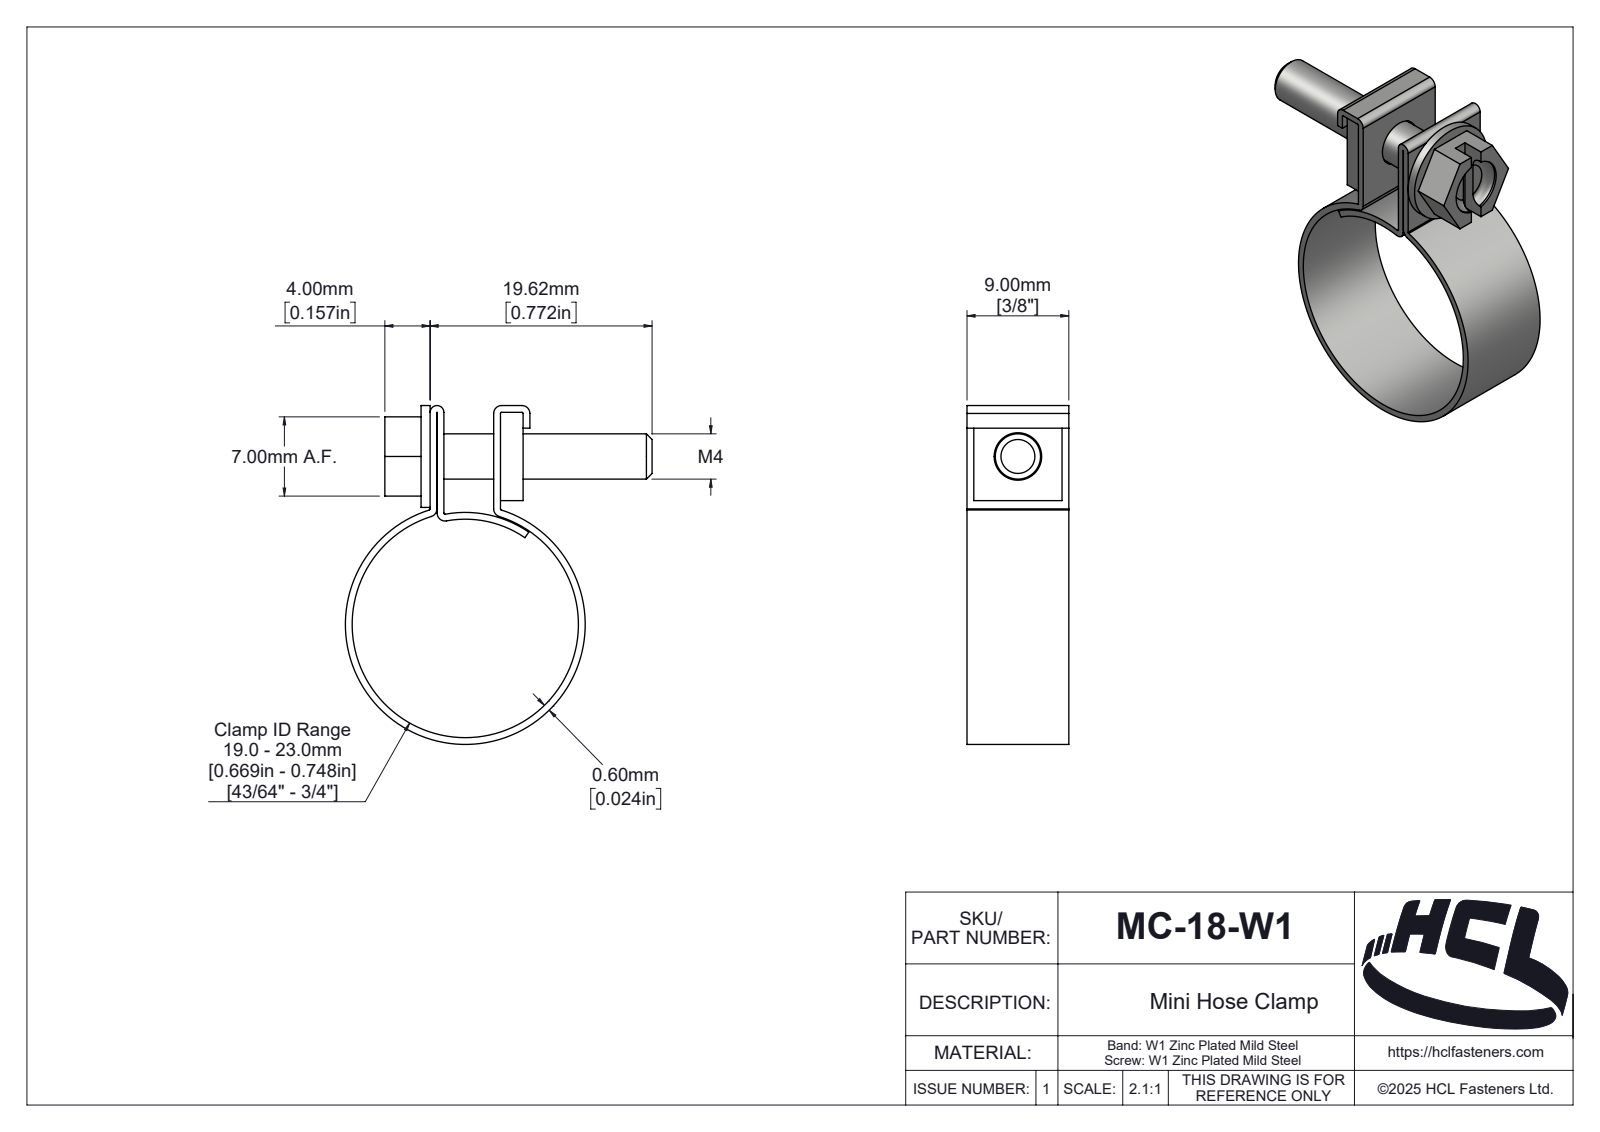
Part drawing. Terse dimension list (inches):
name: MC-18-W1
written by: SolidWorks 2025 (AUTOMOTIVE_DESIGN)
unit: in
bodies: 3 solids, 175 faces (38 planar, 84 cylindrical, 53 other)
size: 1.179 × 1.067 × 0.354
volume: 0.061 in³; area: 3.918 in²
holes: 1× ⌀0.165, 1× ⌀0.197, 1× ⌀0.787
bosses: 1× ⌀0.835, 1× ⌀0.354, 1× ⌀0.157
rounds: 5× R0.004, 5× R0.028, 1× R0.008, 1× R0.024, 1× R0.032, 1× R0.04, 1× R0.042, 1× R0.05
face distances: 0.024, 0.024, 0.197, 0.221, 0.245, 0.276, 0.079, 0.102, 0.324, 0.299
